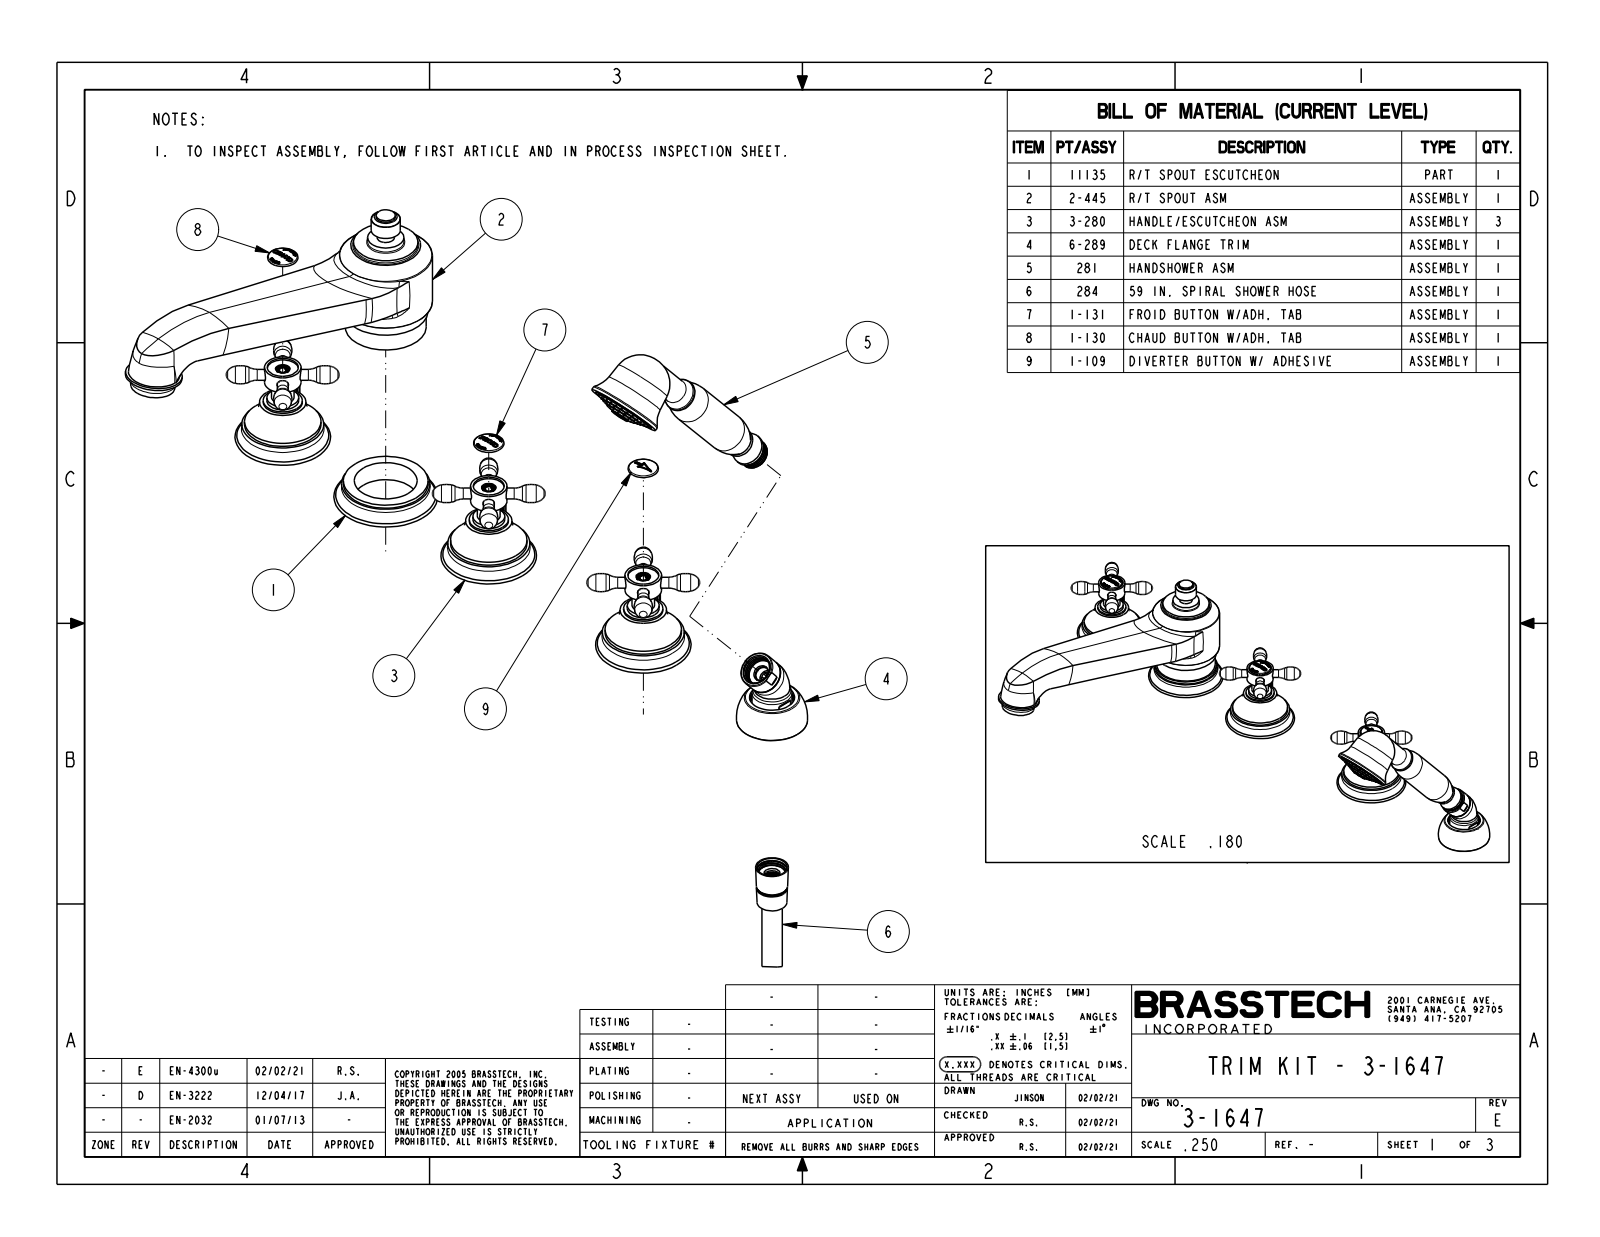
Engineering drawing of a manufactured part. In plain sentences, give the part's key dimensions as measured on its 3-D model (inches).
The part is named "3-1647". Its 3-D file was written by "CREO PARAMETRIC BY PTC INC, 2018400 (CONFIG_CONTROL_DESIGN)". It is 5 solids with 1431 faces: 481 planar, 502 cylindrical and 448 other. Overall it measures 21.353 by 11.211 by 7.234 inches. Its volume is 57.44 cubic inches and its surface area 207.6 square inches. Round holes: 52 of diameter 0.046, 6 of diameter 0.313, 3 of diameter 0.85. Round bosses or shafts: 10 of diameter 0.3, 4 of diameter 1, 3 of diameter 2.1, 3 of diameter 1.075, 3 of diameter 0.875, 3 of diameter 0.625, 3 of diameter 0.4, 2 of diameter 0.9. Partial cylindrical surfaces (rounded edges, fillets, slot ends): 28 of radius 0.011, 17 of radius 0.025, 16 of radius 0.015, 14 of radius 0.006, 10 of radius 0.005, 9 of radius 0.014, 8 of radius 0.006, 8 of radius 0.013. The main face-to-face distances are 0.475, 3.42, 2.945, 0.9, 1.375, 2.045, 0.1, 0.8, 1.225, 0.75. The hole center spacings are 0.185, 0.367, 0.708, 1.002, 0.187, 0.542, 1.124, 1.227.
